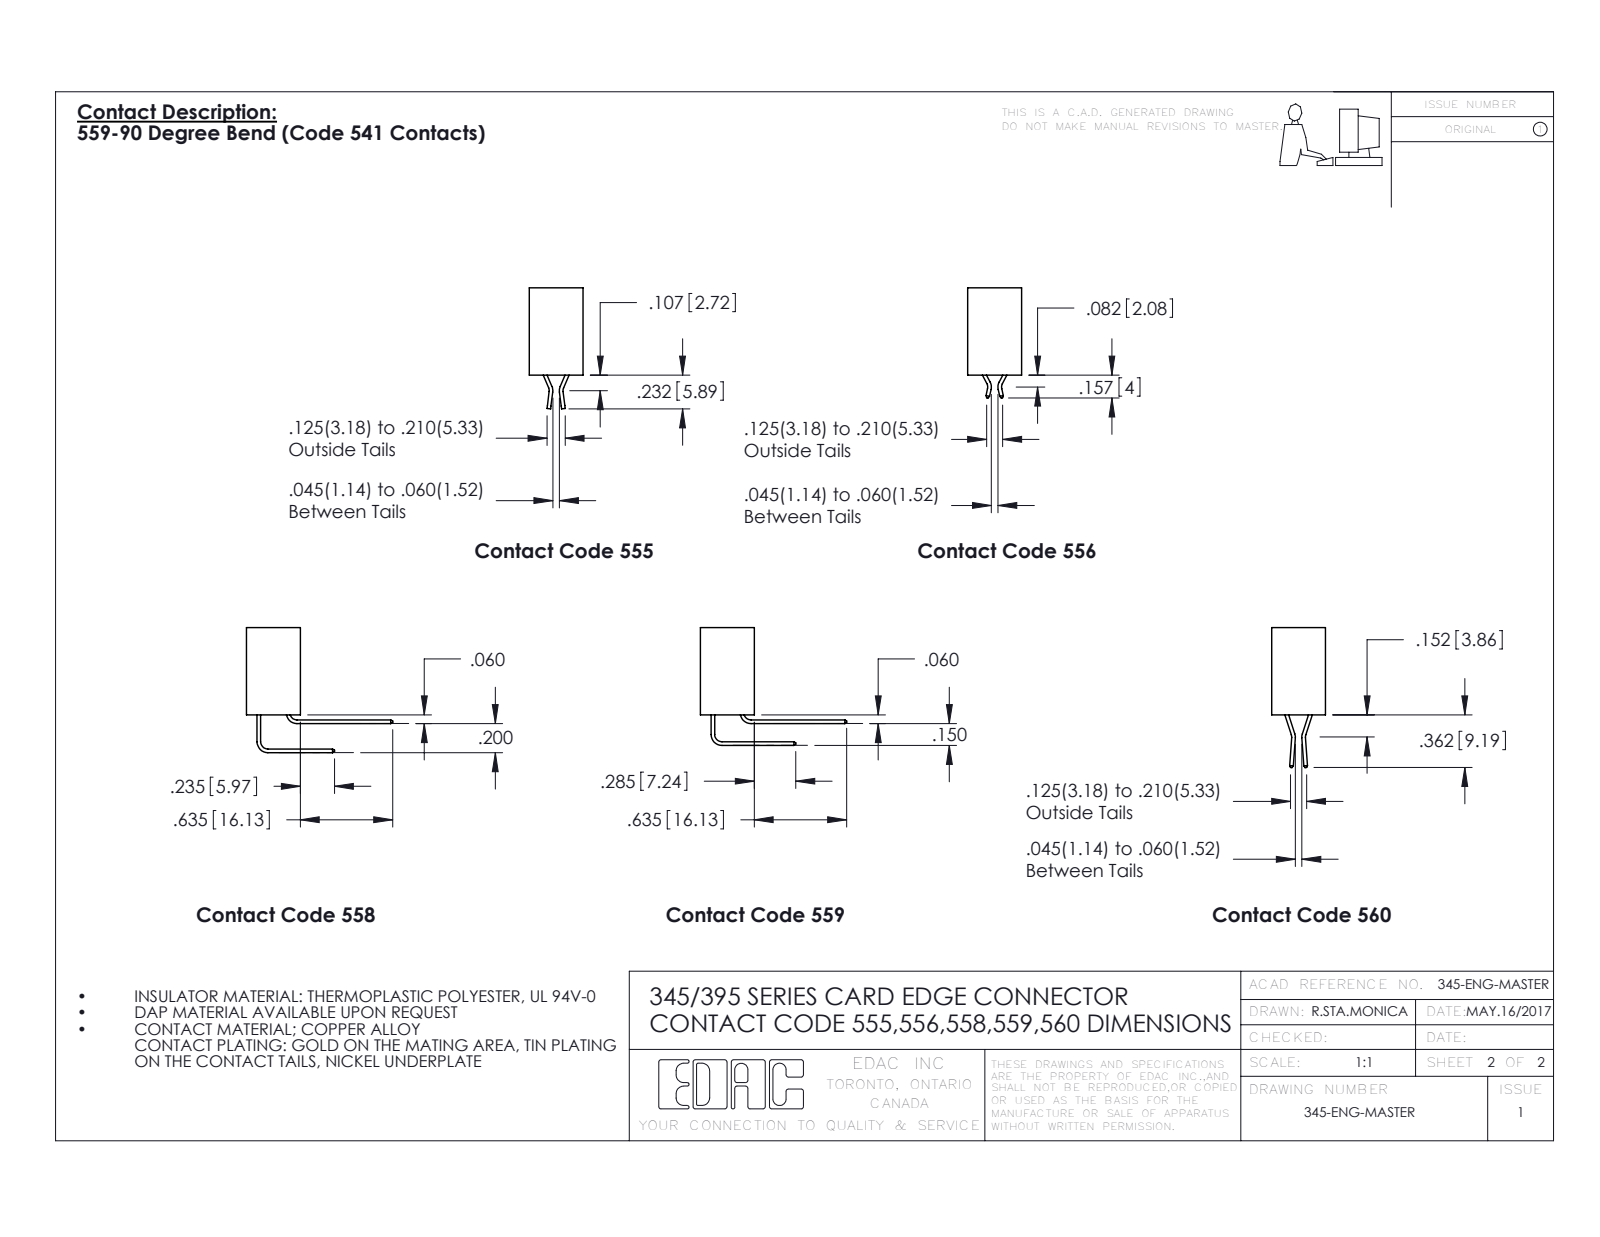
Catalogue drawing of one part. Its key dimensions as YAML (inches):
part_name: "395-138-558-212; 345 Part_Flush Mounting Lugs - Side Mount; 345-292-001_558 559 Tail - 1; 345-292-001_558 Tail - 2"
step_written_by: "SolidWorks 2016 (CONFIG_CONTROL_DESIGN)"
units: inches
bodies: {solids: 139, faces: 7302, planar: 4910, cylindrical: 2392, other: 0}
overall_size: [7.735, 1.005, 0.859]
volume: 1.223
surface_area: 52.33
round_holes:
  - {diameter: 0.128, count: 2}
  - {diameter: 0.064, count: 1}
partial_cylinders:
  - {radius: 0.006, count: 275}
  - {radius: 0.01, count: 22}
  - {radius: 0.007, count: 6}
  - {radius: 0.031, count: 6}
  - {radius: 0.026, count: 3}
  - {radius: 0.014, count: 2}
  - {radius: 0.019, count: 2}
  - {radius: 0.022, count: 2}
face_to_face_distances: [0.072, 0.298, 0.2, 0.37, 0.098, 0.272, 0.025, 0.225, 0.025, 0.175]
hole_center_spacings: [7.475]
